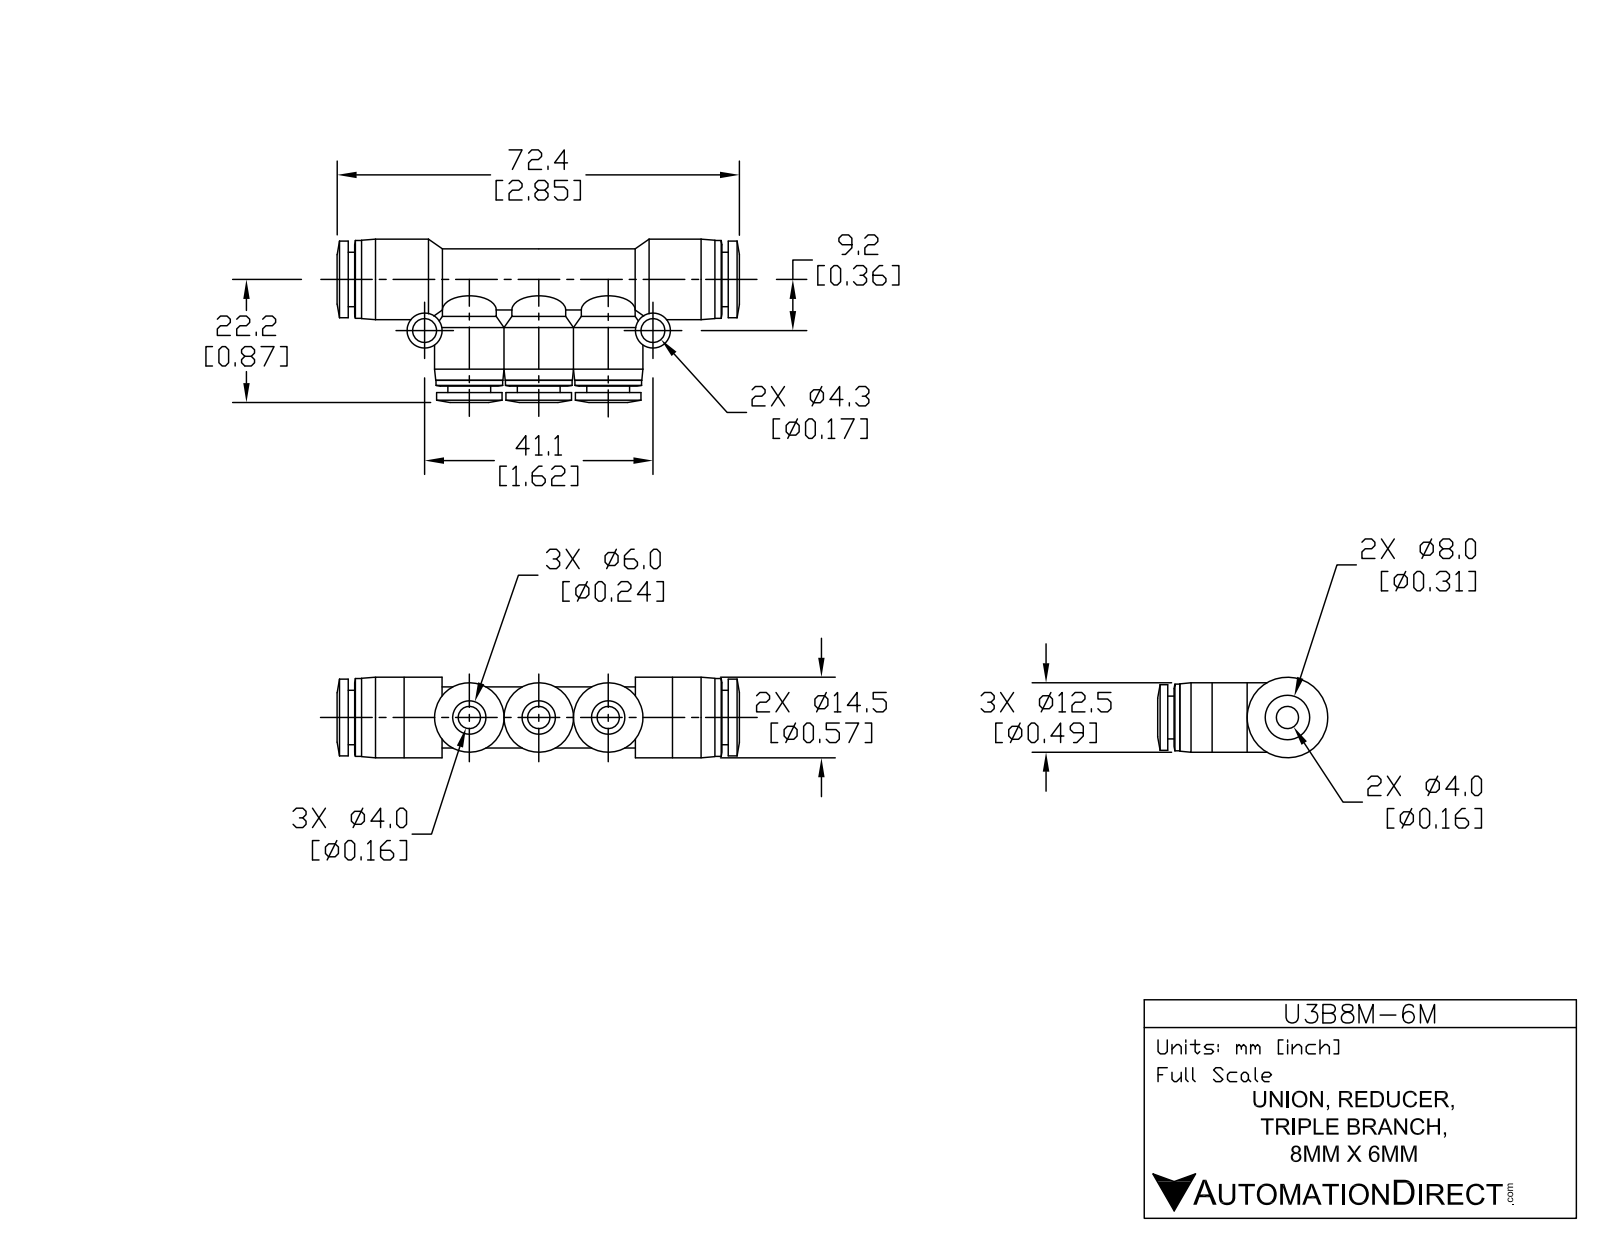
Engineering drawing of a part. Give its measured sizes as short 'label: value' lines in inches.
name: U3B8M-6M
written by: SolidWorks 2015 (AUTOMOTIVE_DESIGN)
unit: in
bodies: 1 solid, 153 faces (29 planar, 74 cylindrical, 50 other)
size: 2.815 × 1.157 × 0.571
volume: 0.631 in³; area: 14.11 in²
holes: 4× ⌀0.197, 3× ⌀0.248, 2× ⌀0.169, 1× ⌀0.327
bosses: 3× ⌀0.492, 3× ⌀0.472, 3× ⌀0.465, 3× ⌀0.382, 3× ⌀0.303, 2× ⌀0.248, 1× ⌀0.571, 1× ⌀0.551
face distances: 0.045, 2.612, 2.657, 0.642, 2.016, 0.596, 1.97, 2.567, 0.53, 0.575
hole spacings: 0.492, 0.984, 1.618
